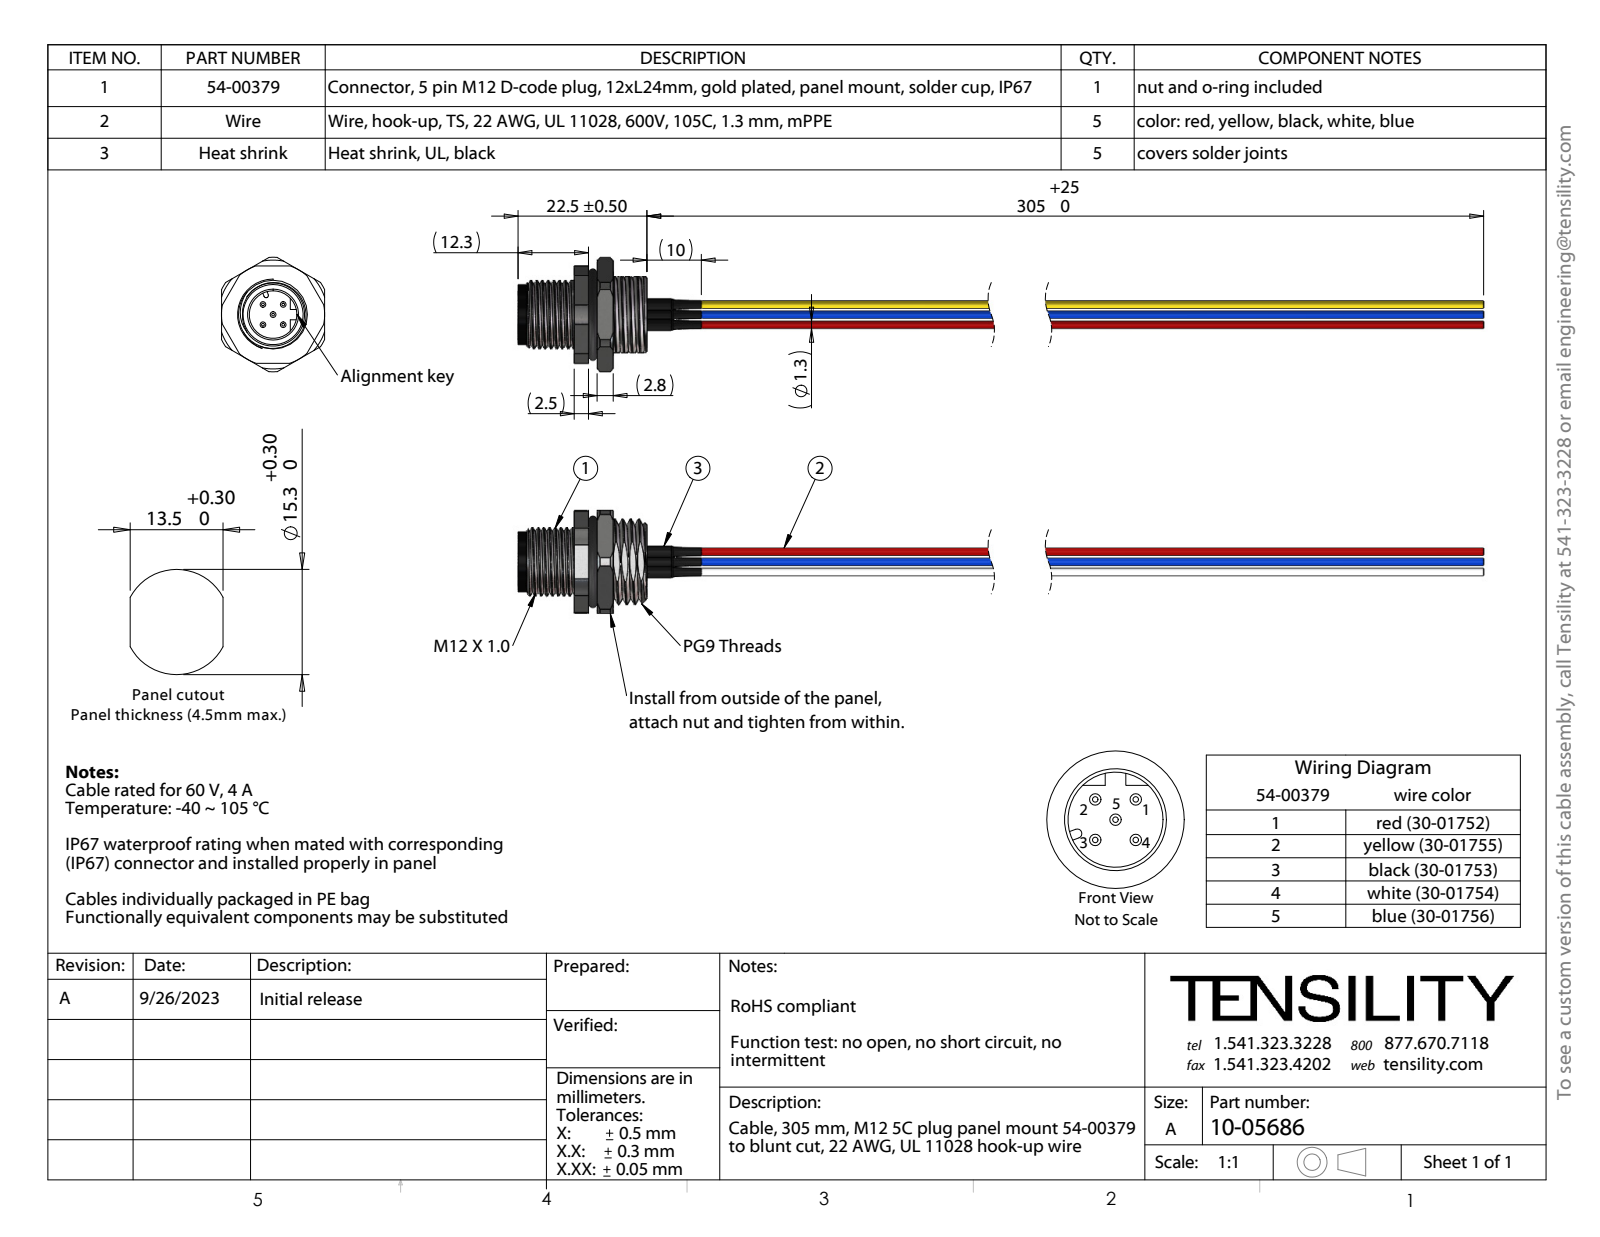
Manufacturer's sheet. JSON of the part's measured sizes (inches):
{"part_name": "10-05686; 54-00379-02; 54-00379-04; 54-00379-05 (+8 more)", "step_written_by": "SolidWorks 2021 (AUTOMOTIVE_DESIGN)", "units": "inches", "bodies": {"solids": 105, "faces": 954, "planar": 286, "cylindrical": 533, "other": 135}, "overall_size": [6.772, 0.787, 0.709], "volume_in3": 0.251, "surface_area_in2": 33.86, "round_holes": [[0.031, 5], [0.039, 5], [0.315, 1], [0.327, 1], [0.366, 1], [0.433, 1], [0.551, 1]], "round_bosses_or_shafts": [[0.079, 5], [0.055, 5], [0.051, 5], [0.512, 1], [0.472, 1], [0.413, 1], [0.354, 1]], "partial_cylinders_radius": [[0.077, 3], [0.016, 1], [0.295, 1], [0.354, 1], [0.394, 1]], "face_to_face_distances": [0.256, 0.059, 0.138, 0.48, 0.118, 0.098, 0.157, 0.224, 0.323, 0.382], "hole_center_spacings": [0.019, 0.013, 0.012, 0.015, 0.133, 0.197, 0.186, 0.013]}
